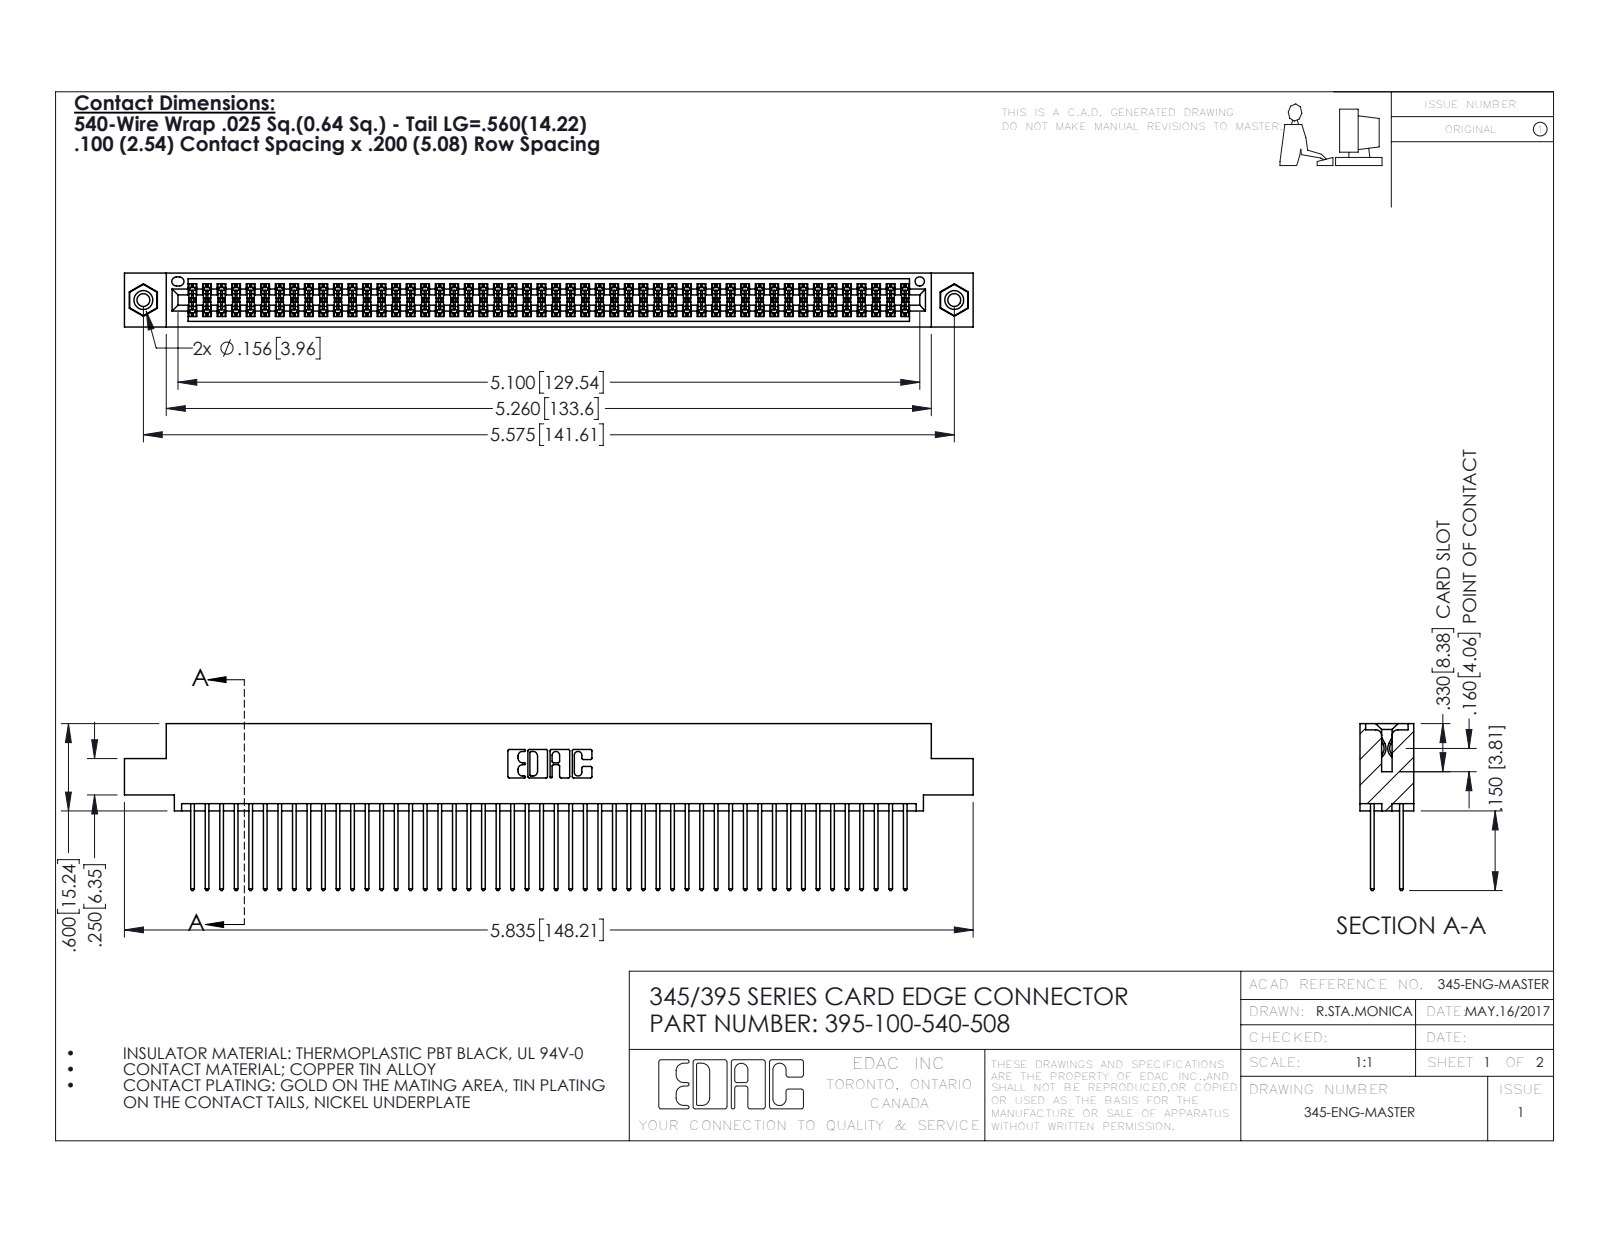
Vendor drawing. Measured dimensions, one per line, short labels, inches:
name: 345-250-001_345-250-003-102; 345-292-001_345-293-140; 395-100-540-508; 345 Part_0.110 Offset - 0.156 Dia-TI
written by: SolidWorks 2016 (CONFIG_CONTROL_DESIGN)
unit: in
bodies: 103 solids, 5190 faces (3416 planar, 1758 cylindrical, 16 other)
size: 5.835 × 1.147 × 0.37
volume: 0.901 in³; area: 36.97 in²
holes: 2× ⌀0.089, 2× ⌀0.125, 2× ⌀0.156, 1× ⌀0.064
bosses: 2× ⌀0.155
rounds: 150× R0.006, 100× R0.01, 22× R0.01, 6× R0.007, 6× R0.031, 3× R0.026, 2× R0.014, 2× R0.019
face distances: 0.072, 0.298, 0.2, 0.098, 0.272, 0.025, 0.37, 0.225, 0.175, 0.149
hole spacings: 0.27, 5.339, 5.575
